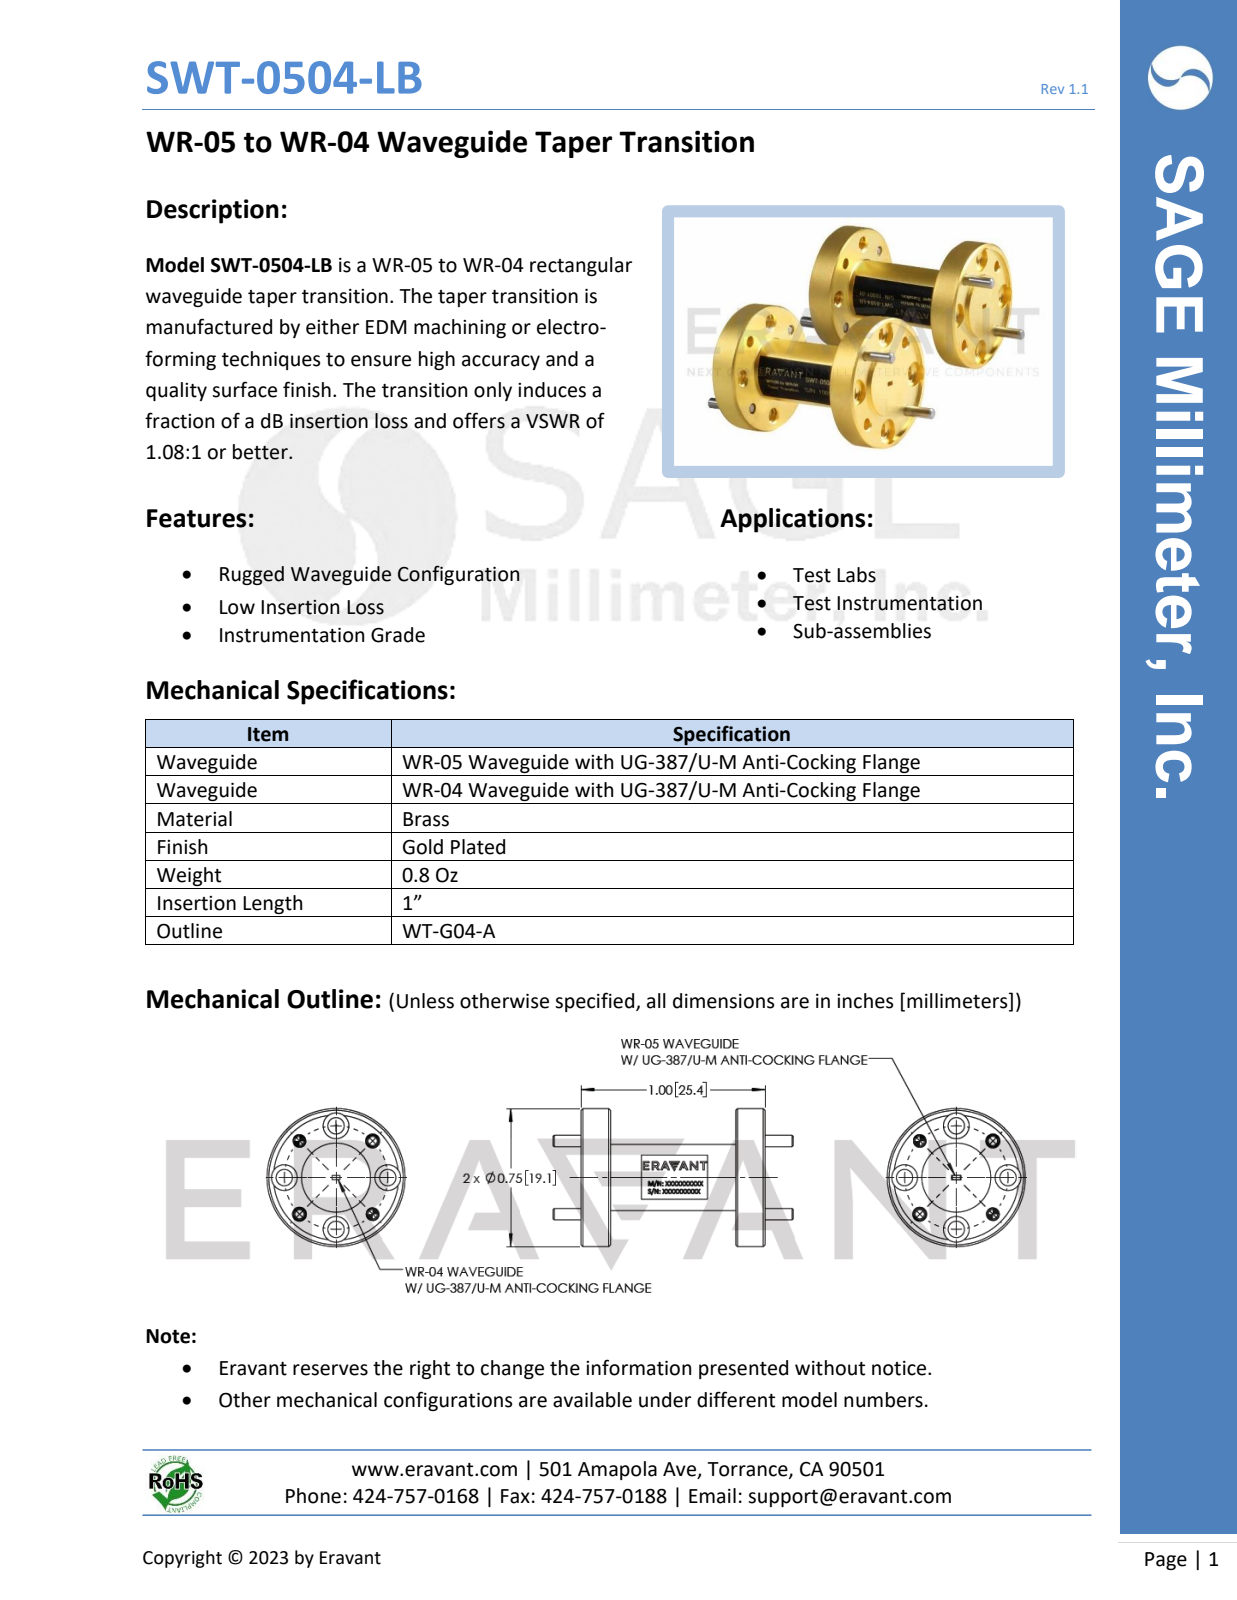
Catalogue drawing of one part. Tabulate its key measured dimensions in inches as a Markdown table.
| quantity | value |
| --- | --- |
| part name | WT-G04-A, Defeatured |
| STEP written by | SolidWorks 2021 (AUTOMOTIVE_DESIGN) |
| units | inches |
| bodies | 5 solids, 148 faces (34 planar, 74 cylindrical, 40 other) |
| overall size | 1.305 × 0.75 × 0.75 |
| volume | 0.19 in³ |
| surface area | 3.866 in² |
| round holes (diameter × count) | 0.061 × 4, 0.067 × 4, 0.089 × 4, 0.14 × 4, 0.68 × 1 |
| round bosses / shafts (diameter × count) | 0.063 × 4, 0.75 × 1, 0.375 × 1, 0.36 × 1 |
| main face-to-face distances | 0.14, 0.82, 0.68, 0.96, 0.98, 0.02, 0.16, 0.84, 0.98, 1 |
| hole center spacings | 0.215, 0.52, 0.398, 0.281, 0.281, 0.563, 0.398, 0.216 |
